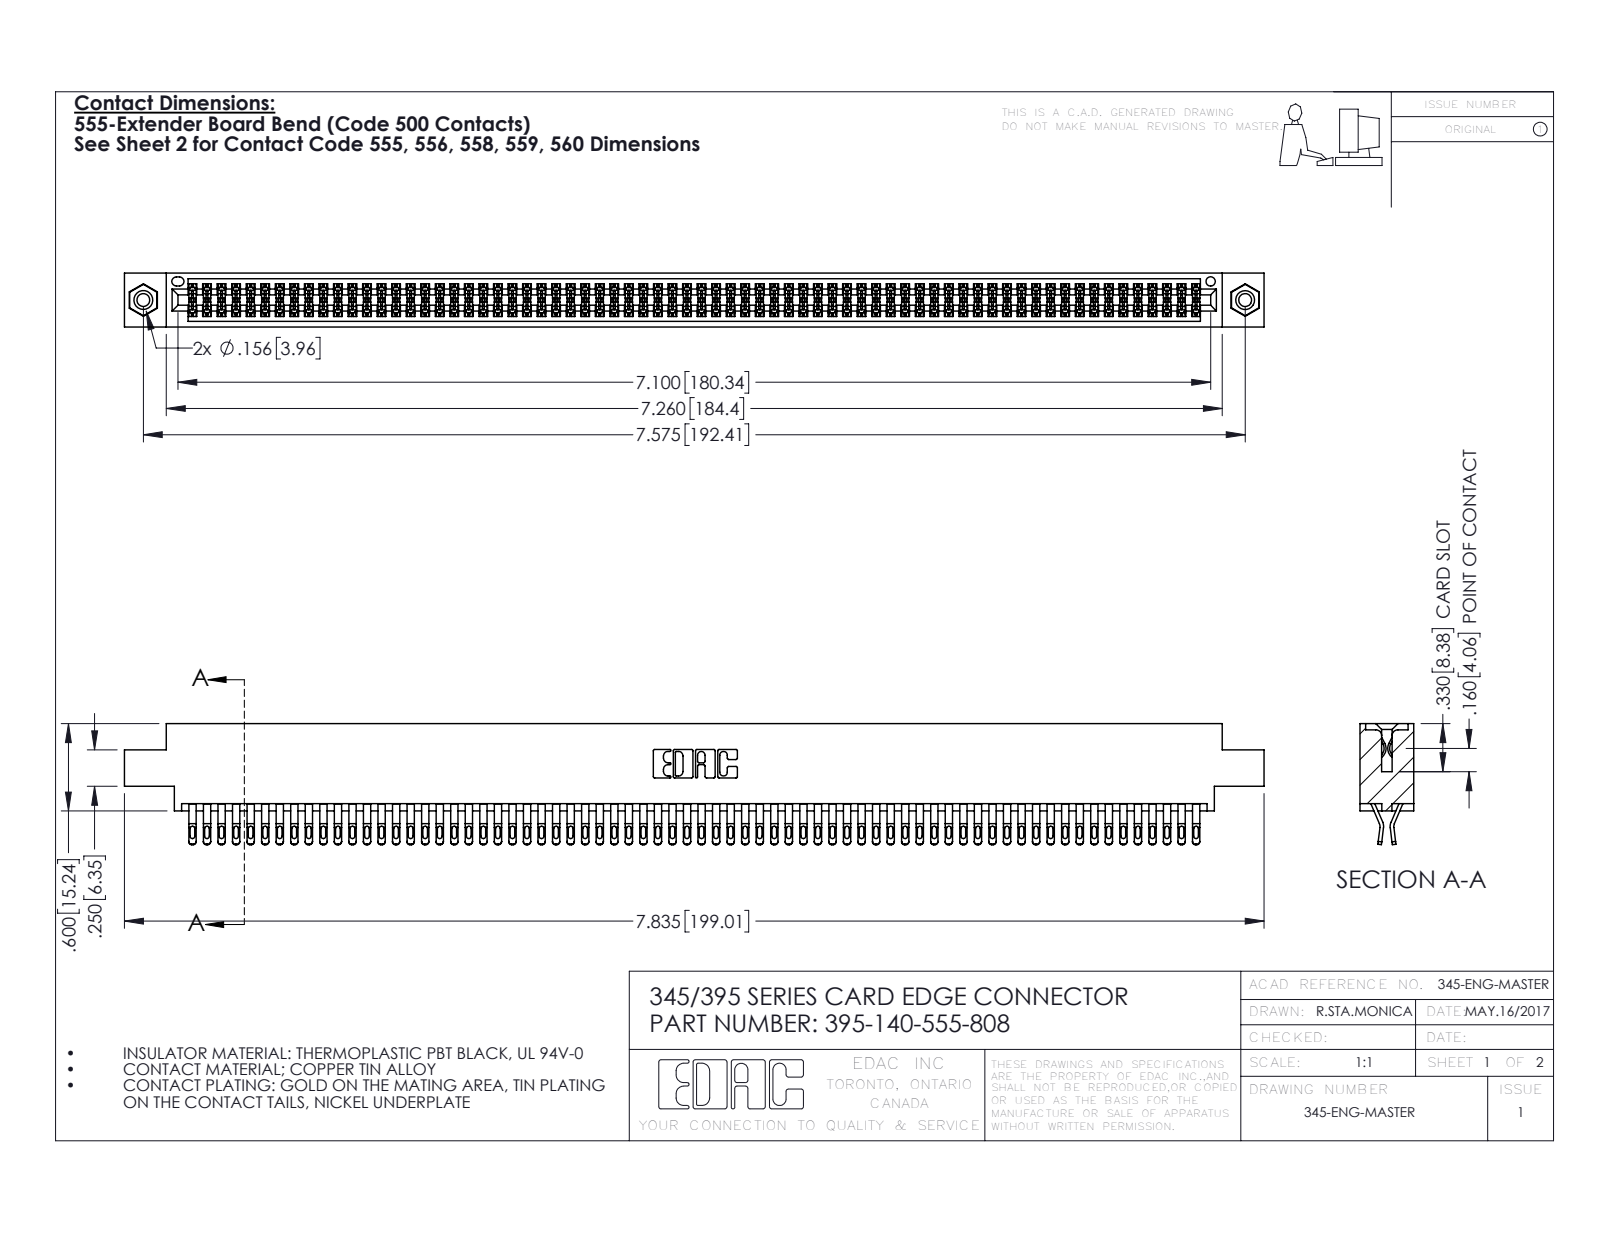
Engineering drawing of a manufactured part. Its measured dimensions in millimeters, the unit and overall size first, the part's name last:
Units: millimetres
Overall size (bounding box): 199 × 21.1 × 9.4
Round holes (diameter × count): ⌀2.3 ×2, ⌀3.2 ×2, ⌀4 ×2, ⌀1.6 ×1
Round bosses / shafts (diameter × count): ⌀3.9 ×2
Partial cylindrical surfaces — rounded edges, fillets, slot ends (radius × count): R0.4 ×350, R0.5 ×280, R0.2 ×210, R0.3 ×22, R0.2 ×6, R0.8 ×6, R0.7 ×3, R0.3 ×2
Main face-to-face distances: 1.8, 7.6, 0.6, 9.4, 5.1, 2.5, 6.9, 5.7, 4.4, 3.8
Hole centre spacings: 6.9, 186.4, 192.4
Volume: 19 880 mm³ · Surface area: 31 500 mm²
Bodies: 143 solids, 8030 faces (4456 planar, 3558 cylindrical, 16 other)
Part name (STEP PRODUCT): 395-140-555-808; 345 Part_0.170 Offset - 0.156 Dia-TI; 345-250-001_345-250-003-102; 345-292-001_555 Tail
STEP written by: SolidWorks 2016 (CONFIG_CONTROL_DESIGN)
